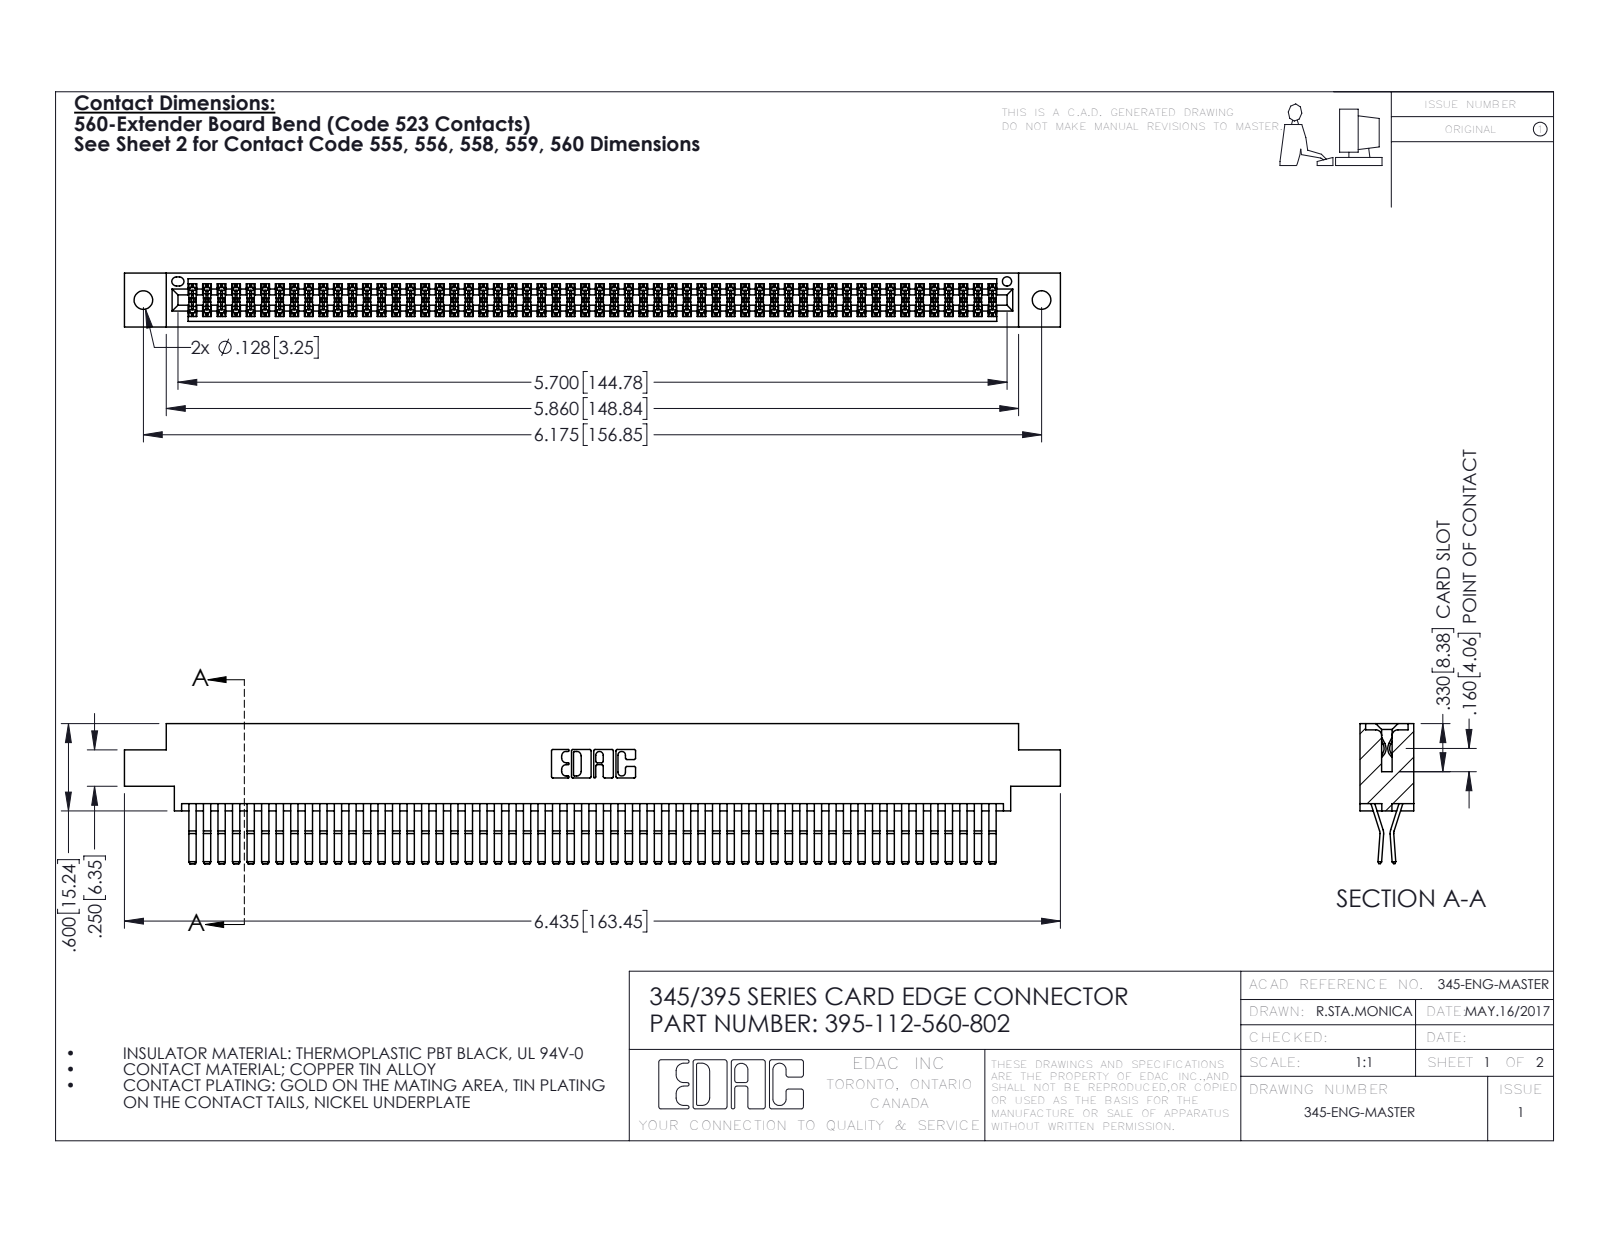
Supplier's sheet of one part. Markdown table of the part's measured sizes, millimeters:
| quantity | value |
| --- | --- |
| part name | 345 Part_0.170 Offset - 0.128 Dia; 395-112-560-802; 345-292-001_560 Tail |
| STEP written by | SolidWorks 2016 (CONFIG_CONTROL_DESIGN) |
| units | millimeters |
| bodies | 113 solids, 5954 faces (3780 planar, 2174 cylindrical, 0 other) |
| overall size | 163.4 × 24.4 × 9.4 |
| volume | 16 580 mm³ |
| surface area | 26 550 mm² |
| round holes (diameter × count) | 3.3 × 2, 1.6 × 1 |
| partial cylindrical surfaces (radius × count) | 0.2 × 168, 0.3 × 22, 0.2 × 6, 0.8 × 6, 0.7 × 3, 0.3 × 2, 0.4 × 2, 0.5 × 2 |
| main face-to-face distances | 0.6, 7.6, 1.8, 9.4, 5.1, 2.5, 6.9, 5.7, 4.4, 3.8 |
| hole center spacings | 6.9, 150.9, 156.8 |
